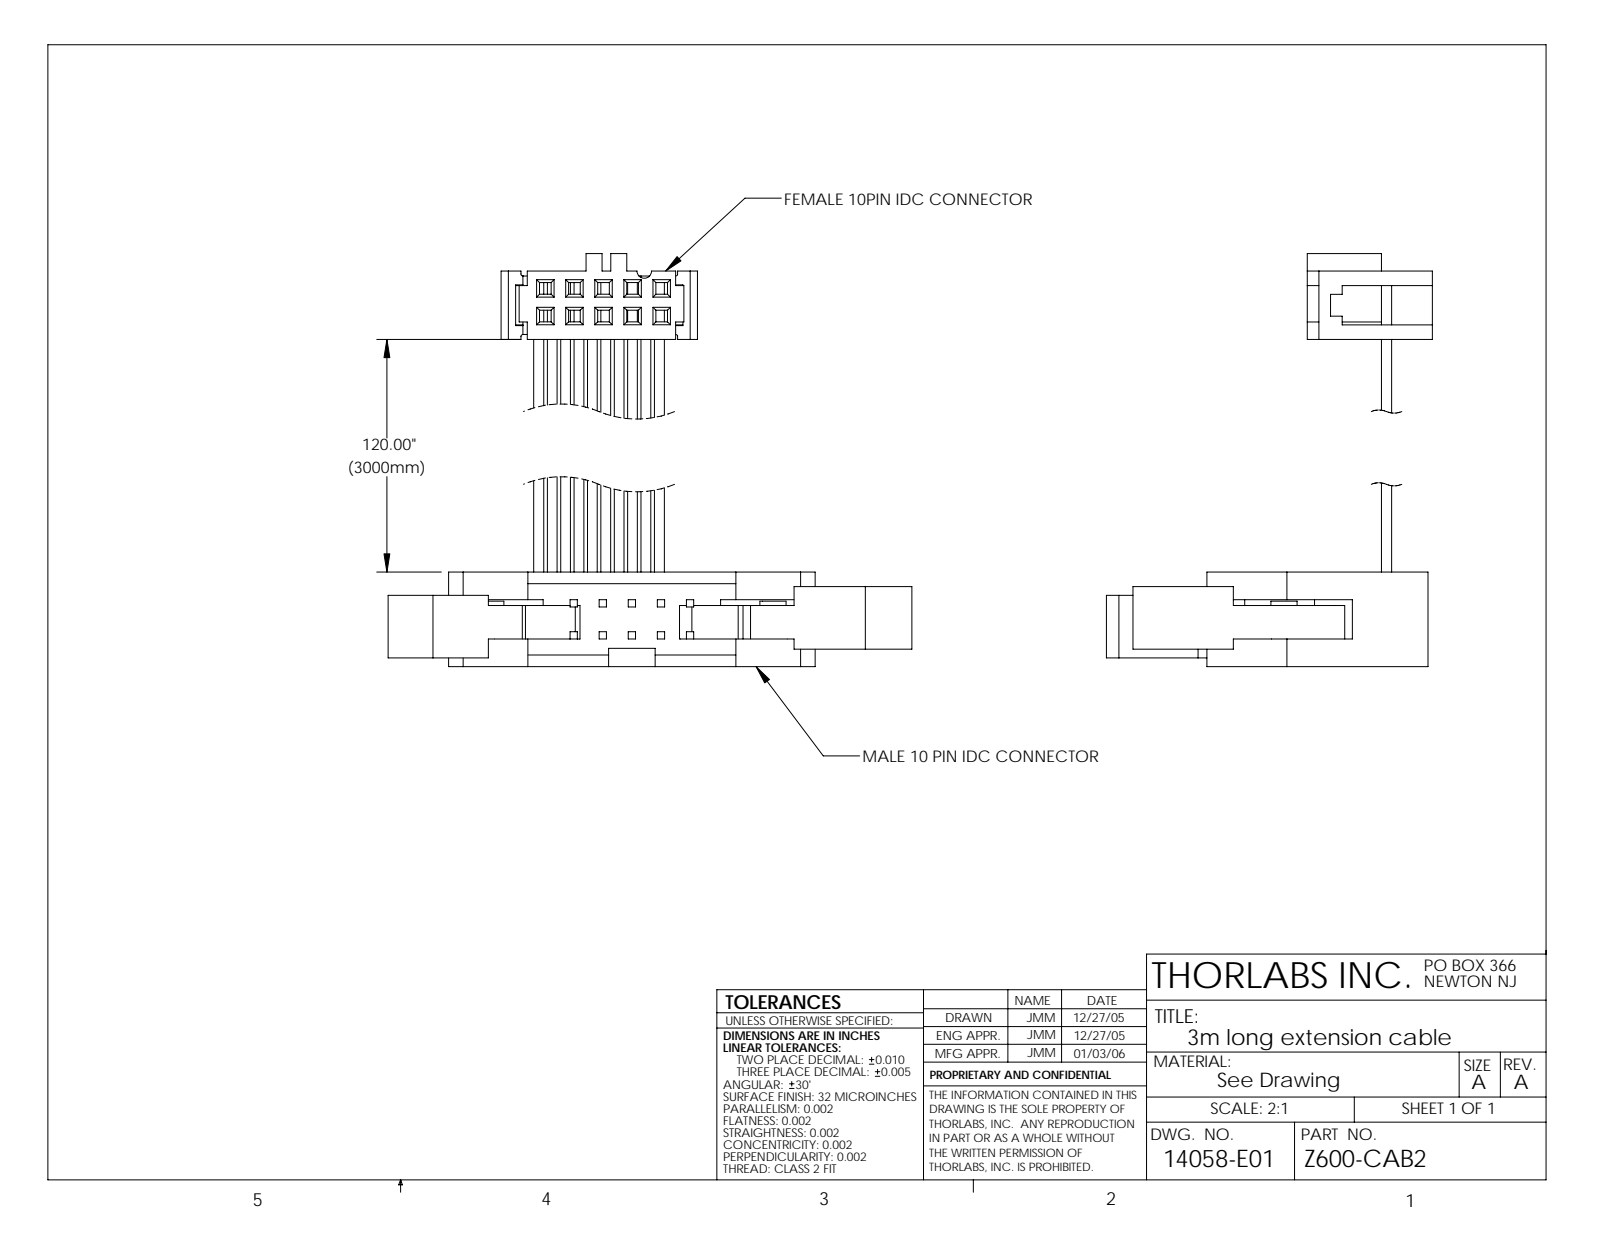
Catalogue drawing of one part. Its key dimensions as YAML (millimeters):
part_name: "14058-E0W"
step_written_by: "SolidWorks 2007 (AUTOMOTIVE_DESIGN)"
units: millimeters
bodies: {solids: 0, faces: 41, planar: 39, cylindrical: 2, other: 0}
overall_size: [3050, 45.7, 28.4]
partial_cylinders:
  - {radius: 0.5, count: 2}
face_to_face_distances: [8.3, 3.8, 7.2, 1, 3042.5, 3035.2, 3034.2, 4.4, 5.8, 1.4]
